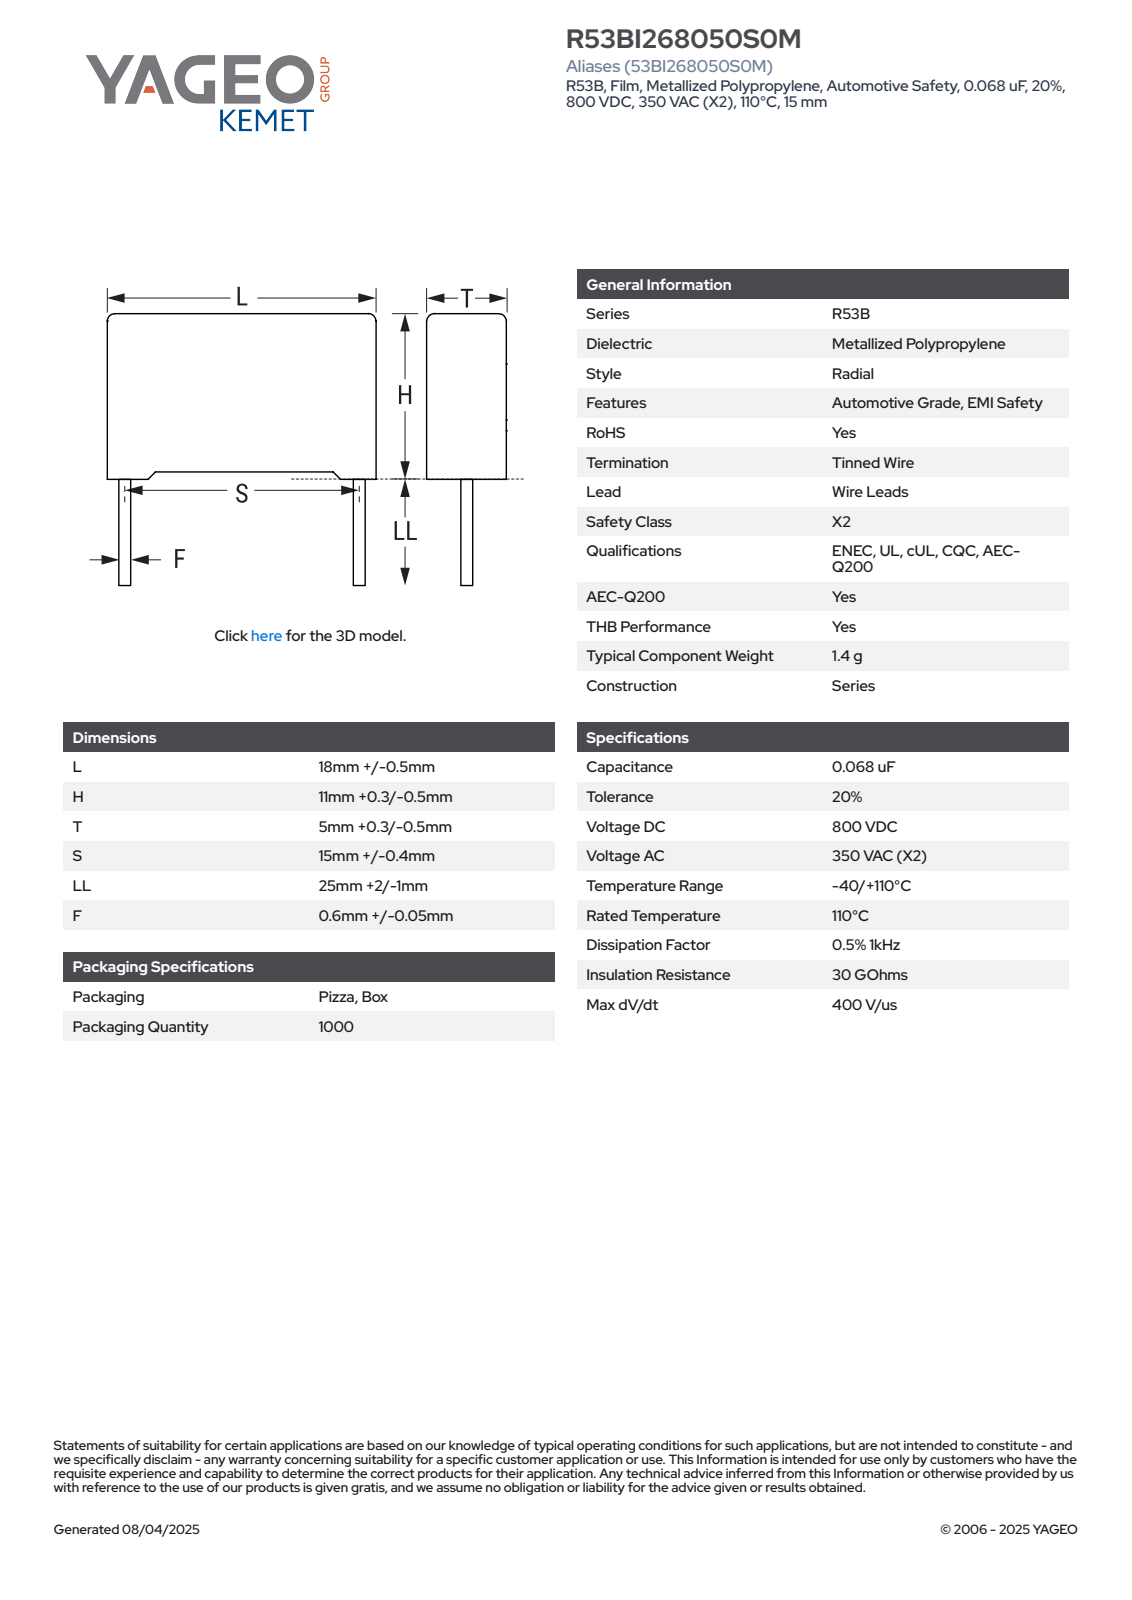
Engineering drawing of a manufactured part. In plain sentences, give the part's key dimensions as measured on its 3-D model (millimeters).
The part is named "CFR_RB2_18X11X5_L18.5H11.3T5.3S15LL27F0.65". Its 3-D file was written by "SolidWorks 2021 (AUTOMOTIVE_DESIGN)". It is 4 solids with 85 faces: 77 planar, 8 cylindrical and 0 other. Overall it measures 38.3 by 18.5 by 5.3 millimeters. Its volume is 1 066 cubic millimeters and its surface area 877 square millimeters. Round bosses or shafts: 2 of diameter 0.65. Partial cylindrical surfaces (rounded edges, fillets, slot ends): 4 of radius 0.5. The main face-to-face distances are 5.3, 10.55, 18.5, 0.62, 4.68, 0.36, 10.91, 0.39, 0.75, 11.3.
